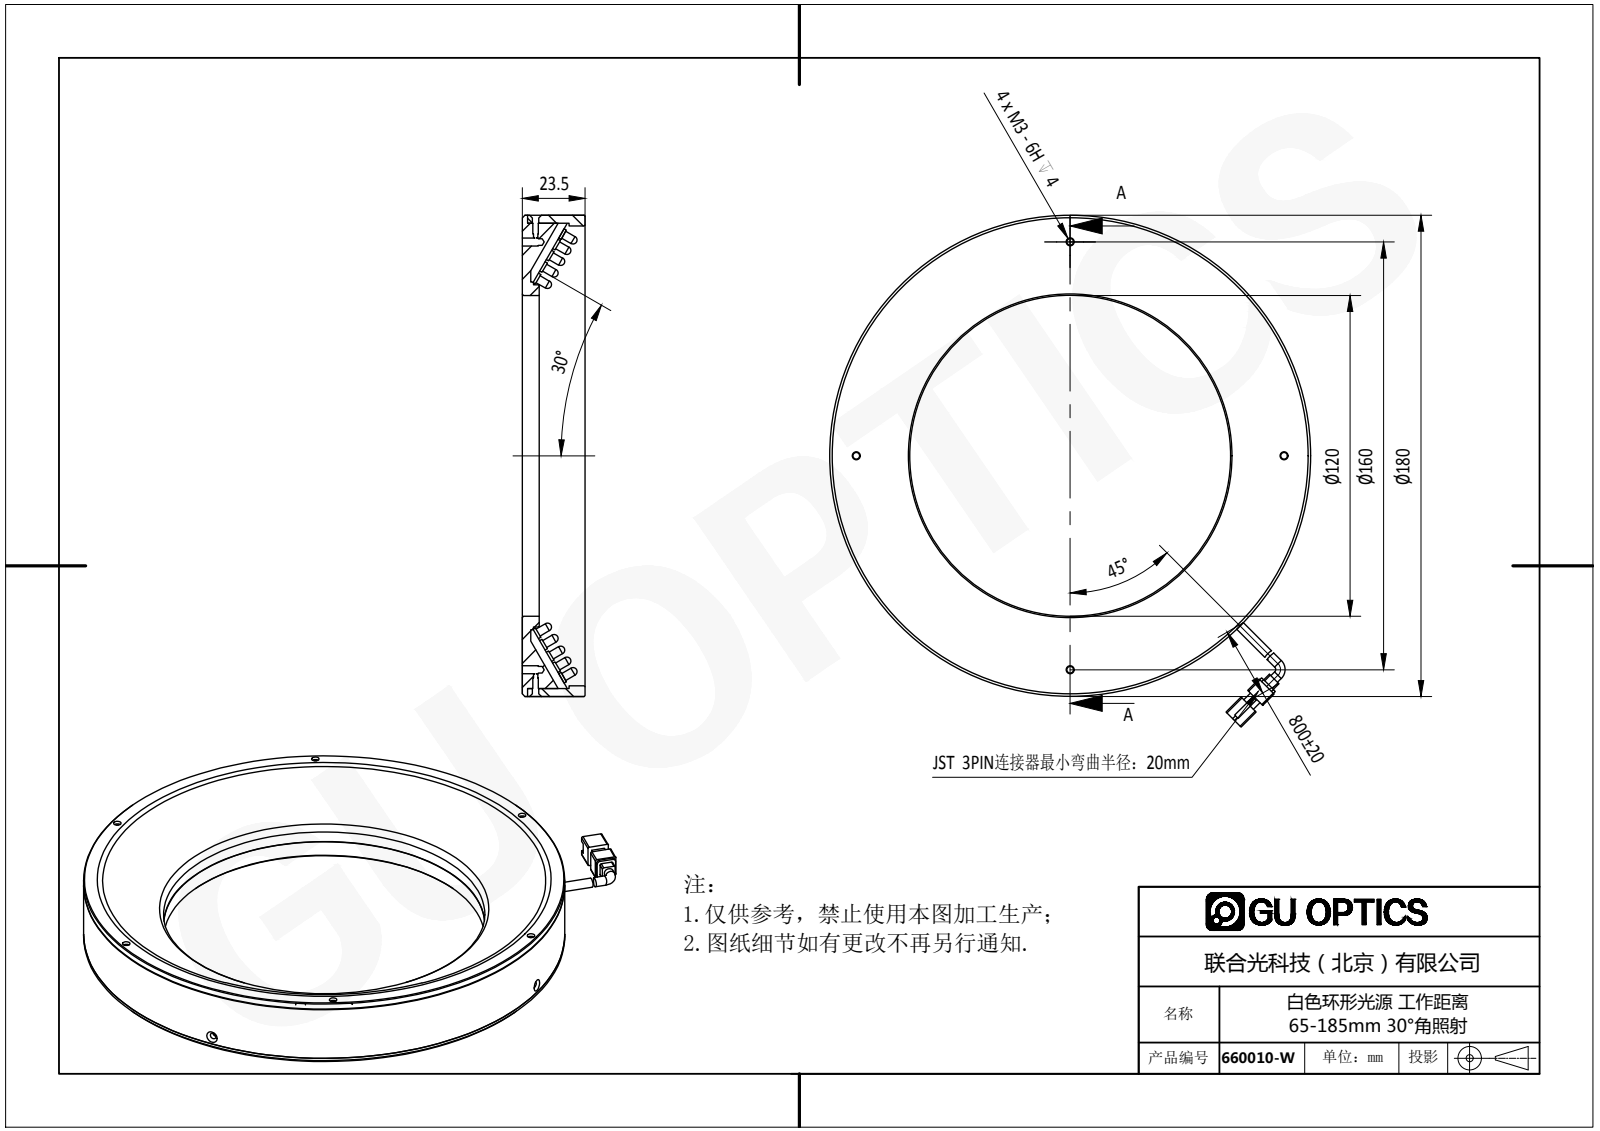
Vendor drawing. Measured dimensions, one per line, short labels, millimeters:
name: 660010-W
written by: SolidWorks 2016 (AUTOMOTIVE_DESIGN)
unit: mm
bodies: 326 solids, 5763 faces (3930 planar, 1439 cylindrical, 394 other)
size: 191.47 × 180 × 26
volume: 194 342 mm³; area: 159 248 mm²
holes: 8× ⌀1.6, 6× ⌀1.25, 6× ⌀1.5, 6× ⌀2.8, 4× ⌀2.5, 4× ⌀3, 4× ⌀3.5, 2× ⌀2, 2× ⌀2.4, 1× ⌀3.6, 1× ⌀120, 1× ⌀120.2
bosses: 320× ⌀3.8, 320× ⌀3, 2× ⌀3.5, 1× ⌀180, 1× ⌀174, 1× ⌀130, 1× ⌀128, 1× ⌀125.2
rounds: 8× R0.5, 4× R1, 1× R9
face distances: 23.5, 2, 21.5, 2.5, 26, 24, 1, 1.22, 3.22, 20.28
hole spacings: 87.5, 151.56, 43.95, 80, 84, 113.14, 118.56, 145.11
